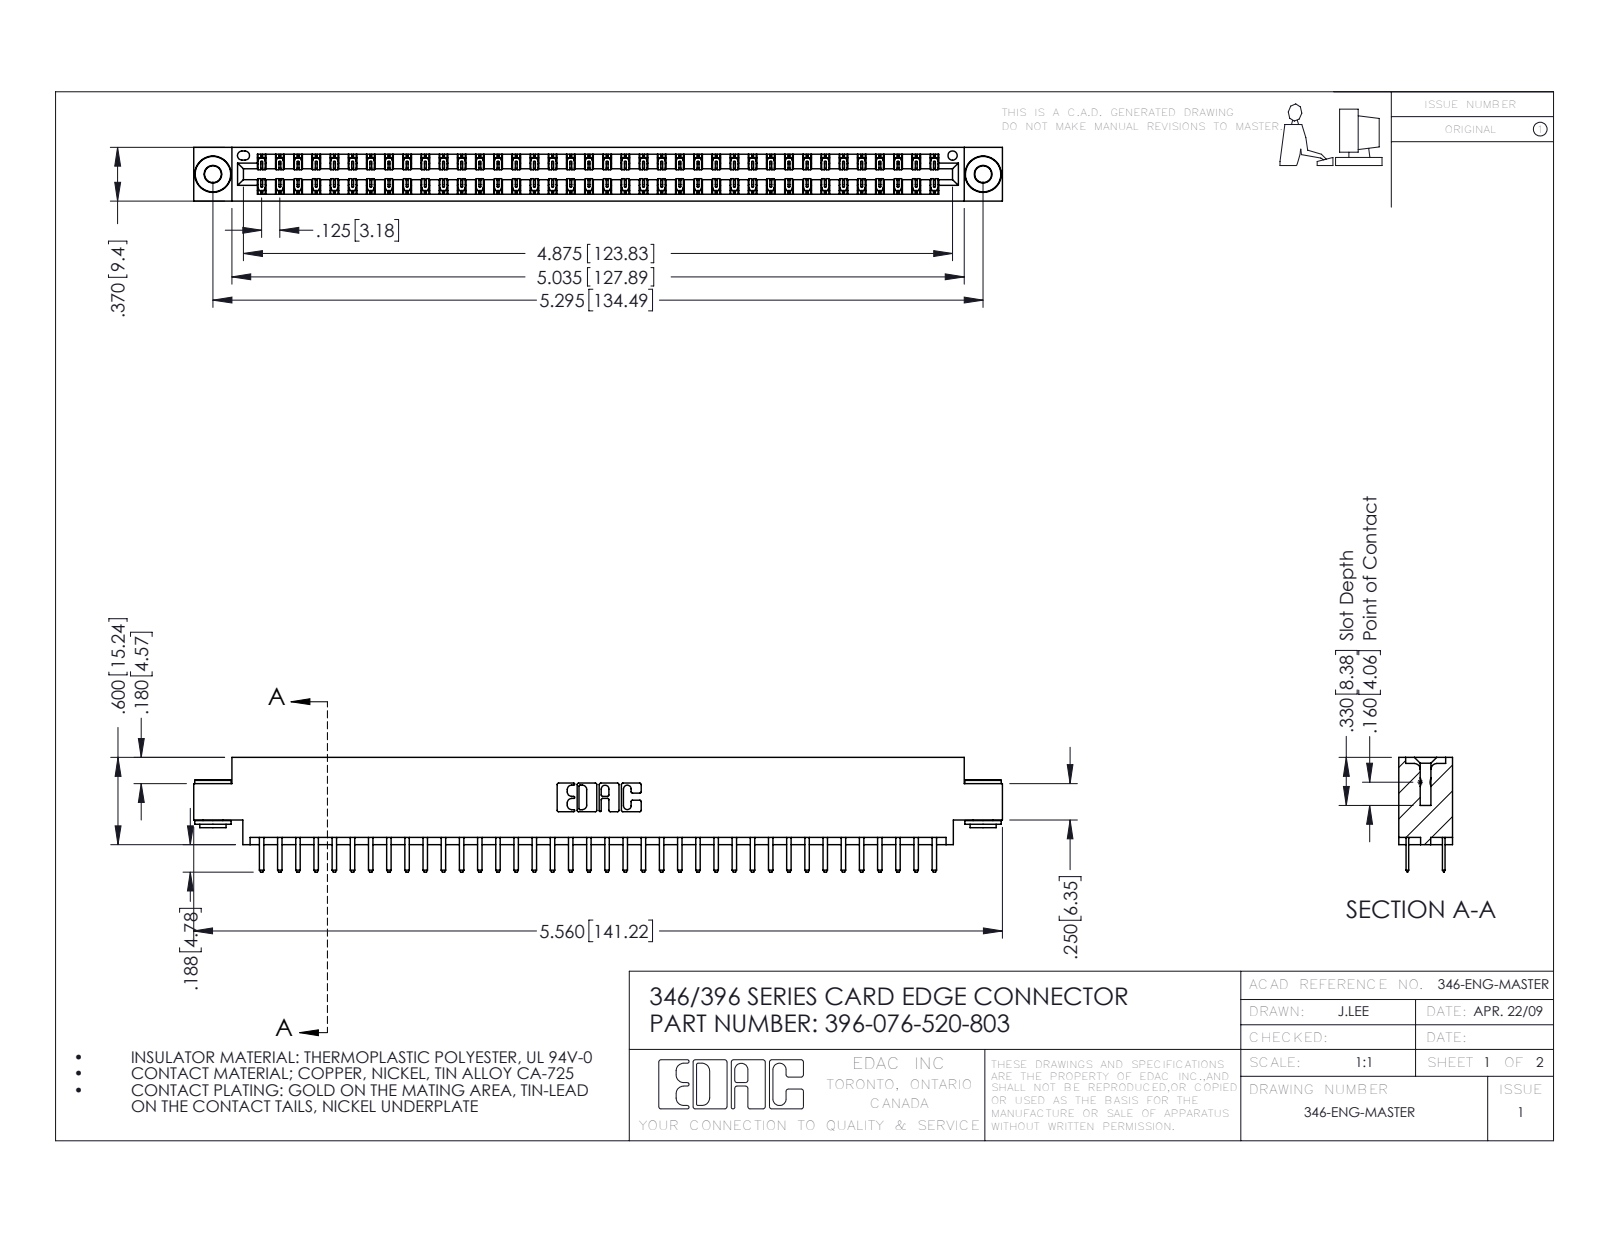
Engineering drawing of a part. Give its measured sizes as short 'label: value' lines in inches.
name: 345-292-001_345-293-120; 396-076-520-803; 345-250-002_345-250-002-102; 346 Part_0.170 Offset - 0.156 Dia-TH
written by: SolidWorks 2016 (CONFIG_CONTROL_DESIGN)
unit: in
bodies: 79 solids, 4420 faces (2902 planar, 1510 cylindrical, 8 other)
size: 5.56 × 0.788 × 0.37
volume: 0.828 in³; area: 29.31 in²
holes: 2× ⌀0.116, 2× ⌀0.156, 1× ⌀0.064
bosses: 2× ⌀0.25, 2× ⌀0.18, 2× ⌀0.136
rounds: 114× R0.006, 80× R0.01, 22× R0.01, 6× R0.007, 6× R0.031, 3× R0.026, 2× R0.014, 2× R0.022
face distances: 0.048, 0.322, 0.25, 0.37, 0.025, 0.275, 0.072, 0.298, 0.148, 0.222
hole spacings: 0.246, 5.086, 5.295
